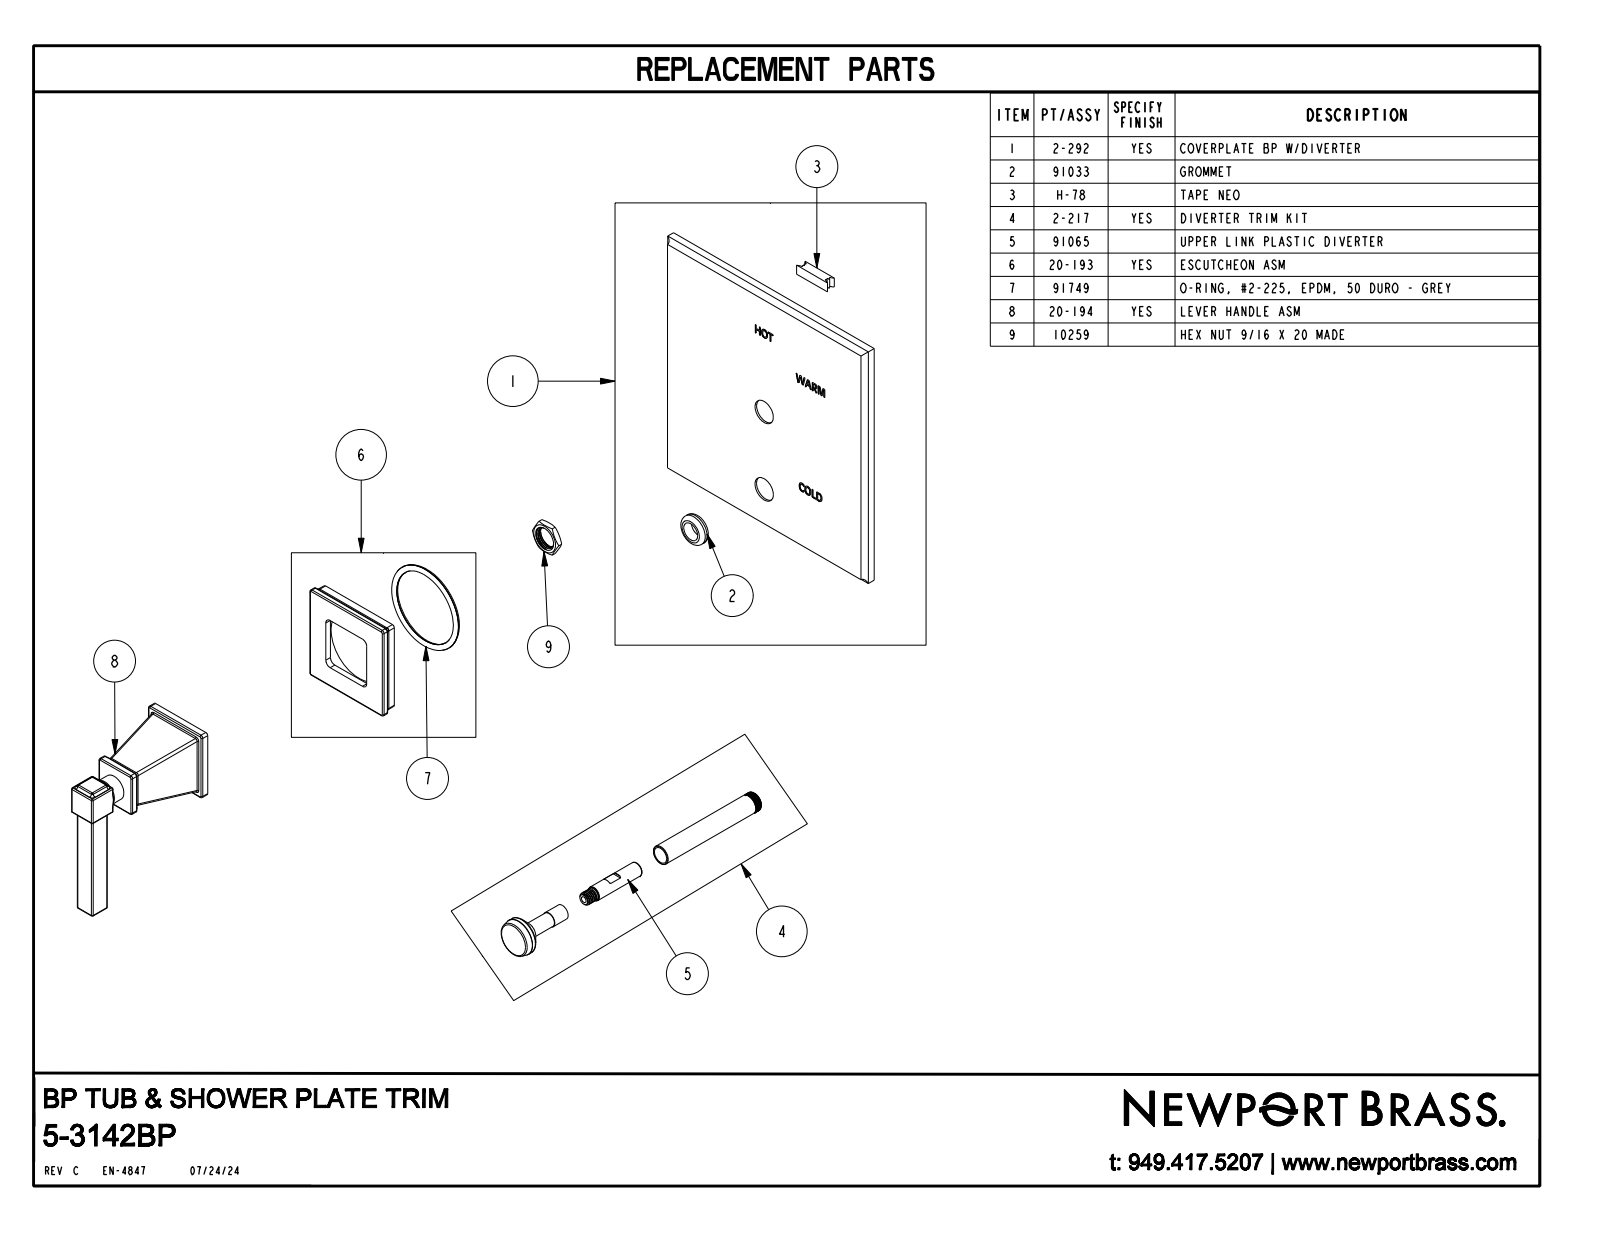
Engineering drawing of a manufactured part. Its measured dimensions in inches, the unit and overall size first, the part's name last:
Units: inches
Overall size (bounding box): 6.5 × 6.5 × 3.941
Round bosses / shafts (diameter × count): ⌀0.9 ×1, ⌀0.625 ×1, ⌀0.506 ×1, ⌀0.354 ×1
Partial cylindrical surfaces — rounded edges, fillets, slot ends (radius × count): R0.03 ×48, R0.06 ×28, R0.09 ×8, R0.125 ×4, R0.23 ×4
Main face-to-face distances: 0.313, 0.723, 0.41, 6.5, 0.5, 3, 3.5, 2.105, 4.395, 0.593
Volume: 19.97 in³ · Surface area: 117.5 in²
Bodies: 1 solid, 426 faces (150 planar, 104 cylindrical, 172 other)
Part name (STEP PRODUCT): 5-3142BP
STEP written by: CREO PARAMETRIC BY PTC INC, 2018400 (CONFIG_CONTROL_DESIGN)
